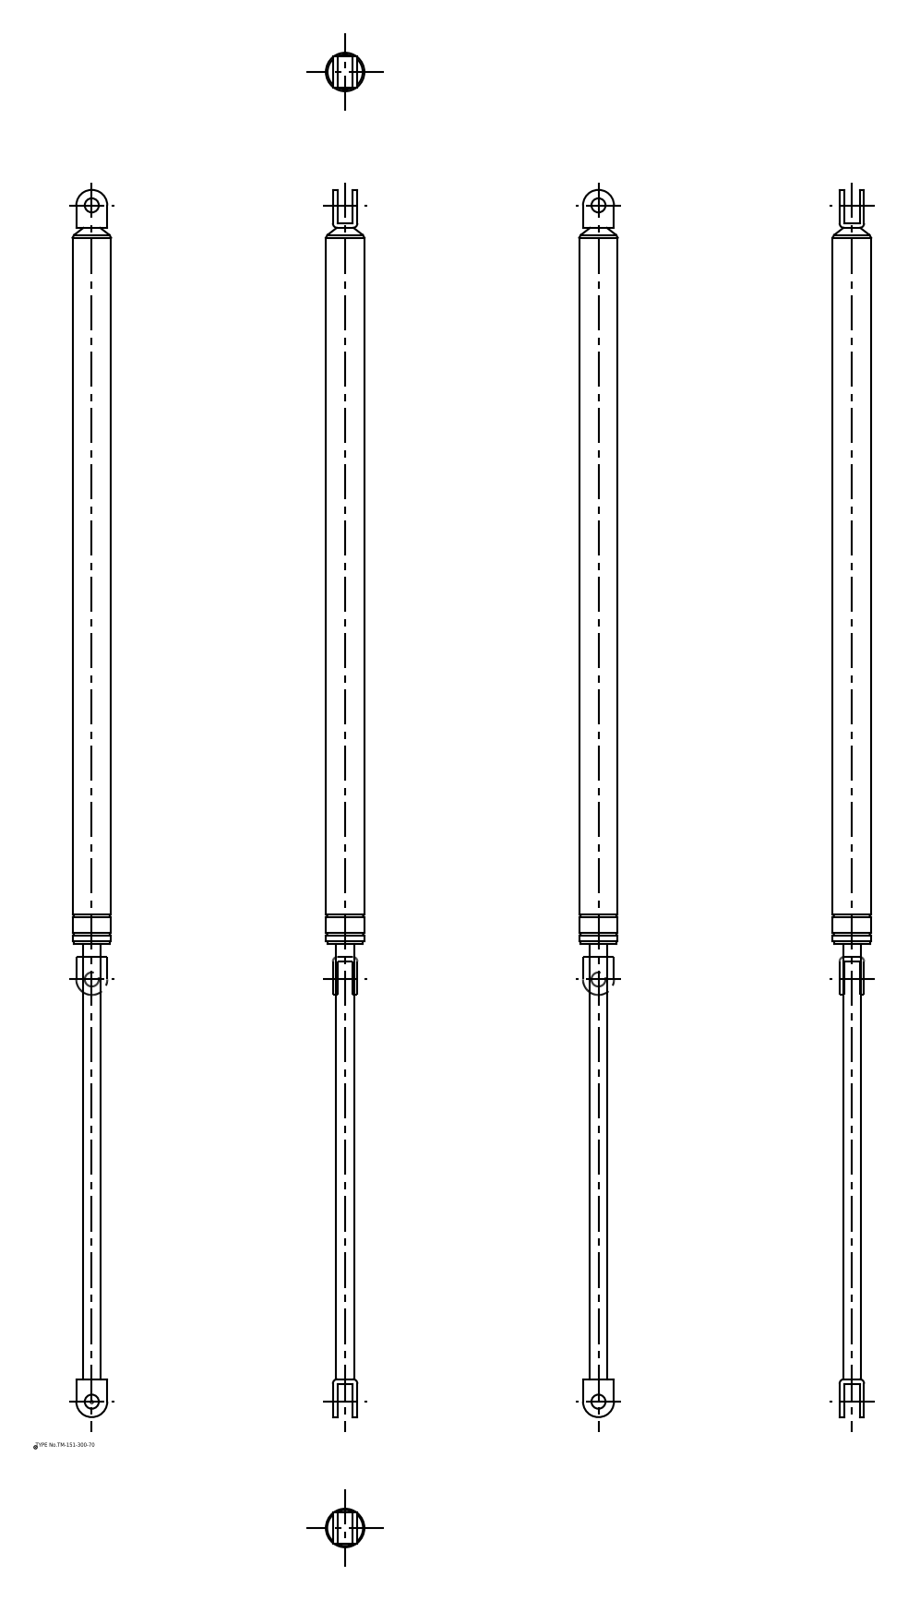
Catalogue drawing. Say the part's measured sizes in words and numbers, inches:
The part is named "TM_151_300_70; TM_151_300_70_div". Its 3-D file was written by "spGate 16.7.1 (AUTOMOTIVE_DESIGN)". It is 2 solids with 64 faces: 22 planar, 32 cylindrical and 10 other. Overall it measures 34.331 by 1.11 by 1.11 inches. Its volume is 20.98 cubic inches and its surface area 97.23 square inches. Round holes: 2 of diameter 0.394. Round bosses or shafts: 1 of diameter 1.11, 1 of diameter 1.079, 1 of diameter 1.004, 1 of diameter 0.492. Partial cylindrical surfaces (rounded edges, fillets, slot ends): 4 of radius 0.126, 2 of radius 0.433. The main face-to-face distances are 0.126, 0.559, 0.685, 0.433, 0.866, 32.331, 12.291, 32.457, 20.165, 20.039. The hole center spacings are 33.465.
